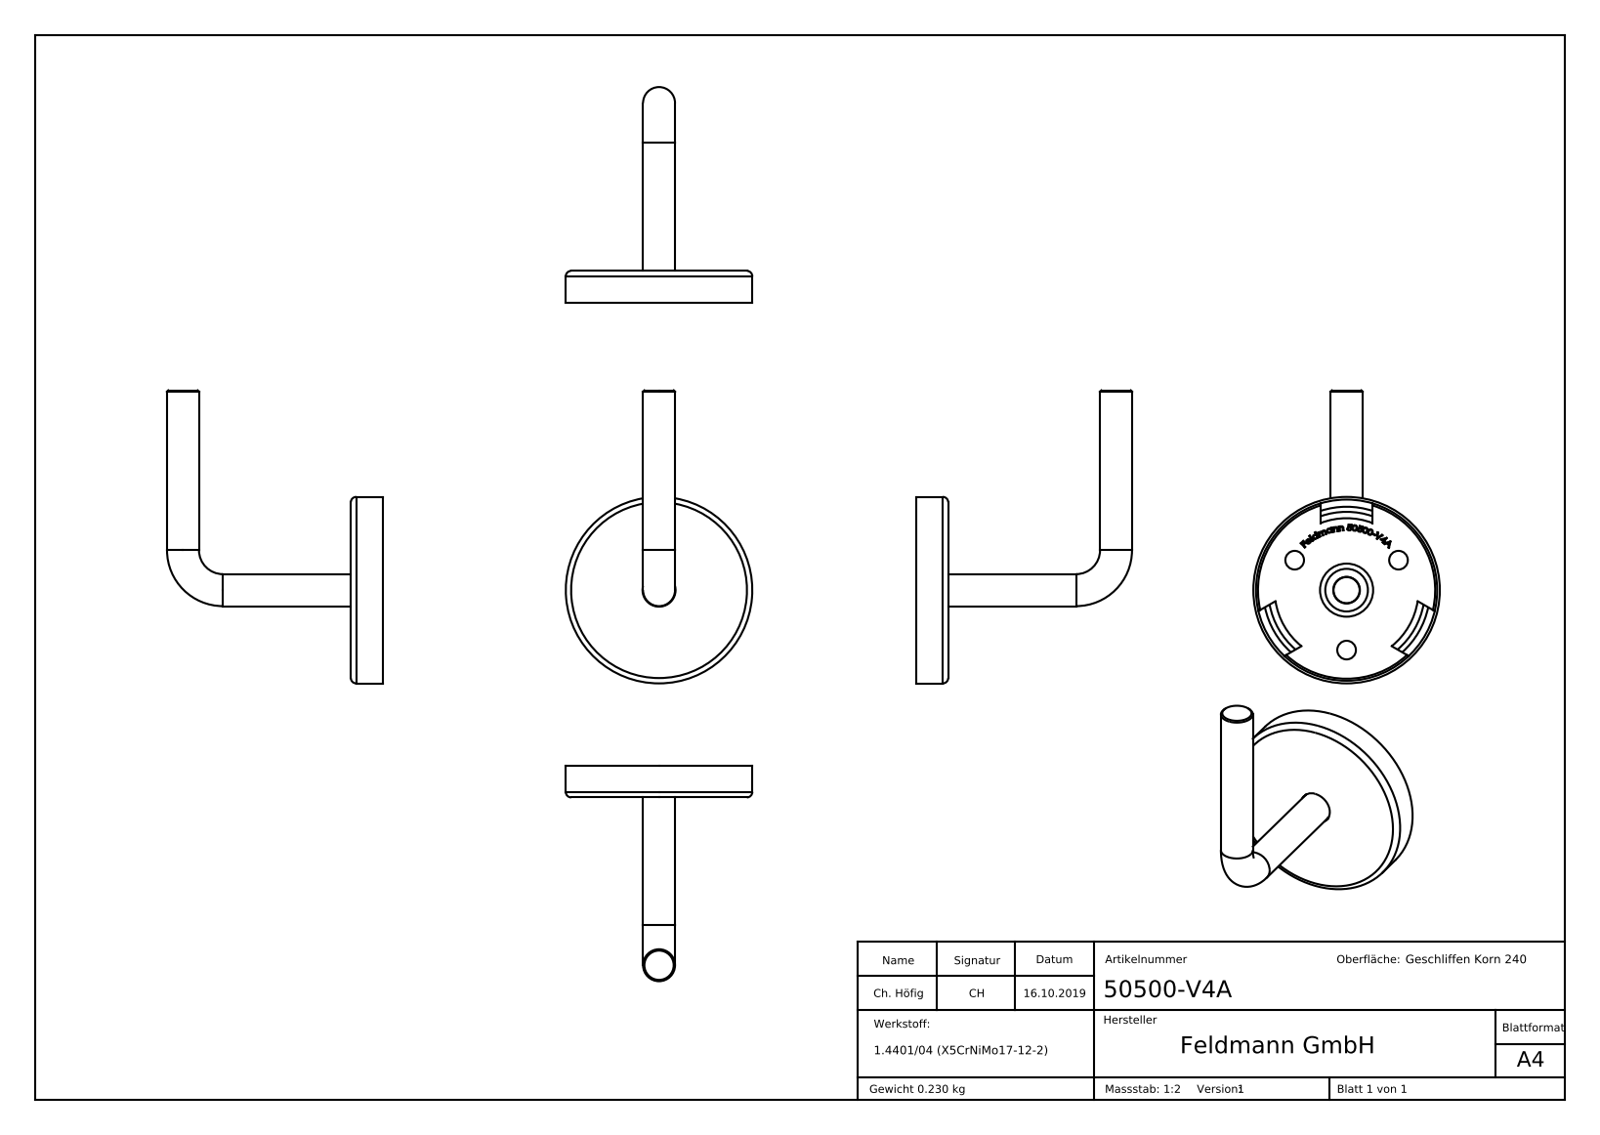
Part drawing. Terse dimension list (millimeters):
name: 5050X-240 Teil3; 50500-V4A; 5050X-240 Teil1_50500-V4A-P; 5050X-240 Teil2_50500-V4A Teil2 (+3 more)
written by: SolidWorks 2015 (CONFIG_CONTROL_DESIGN)
unit: mm
bodies: 3 solids, 279 faces (152 planar, 16 cylindrical, 111 other)
size: 110 × 81 × 70
volume: 28 755 mm³; area: 25 400 mm²
holes: 3× ⌀7, 1× ⌀10, 1× ⌀12.4
bosses: 2× ⌀12, 1× ⌀70, 1× ⌀68, 1× ⌀9.8
rounds: 1× R33.25
face distances: 1, 11, 12, 2, 9, 10, 3.2, 5.2, 5.8, 6.8
hole spacings: 22.5, 38.97, 38.98
